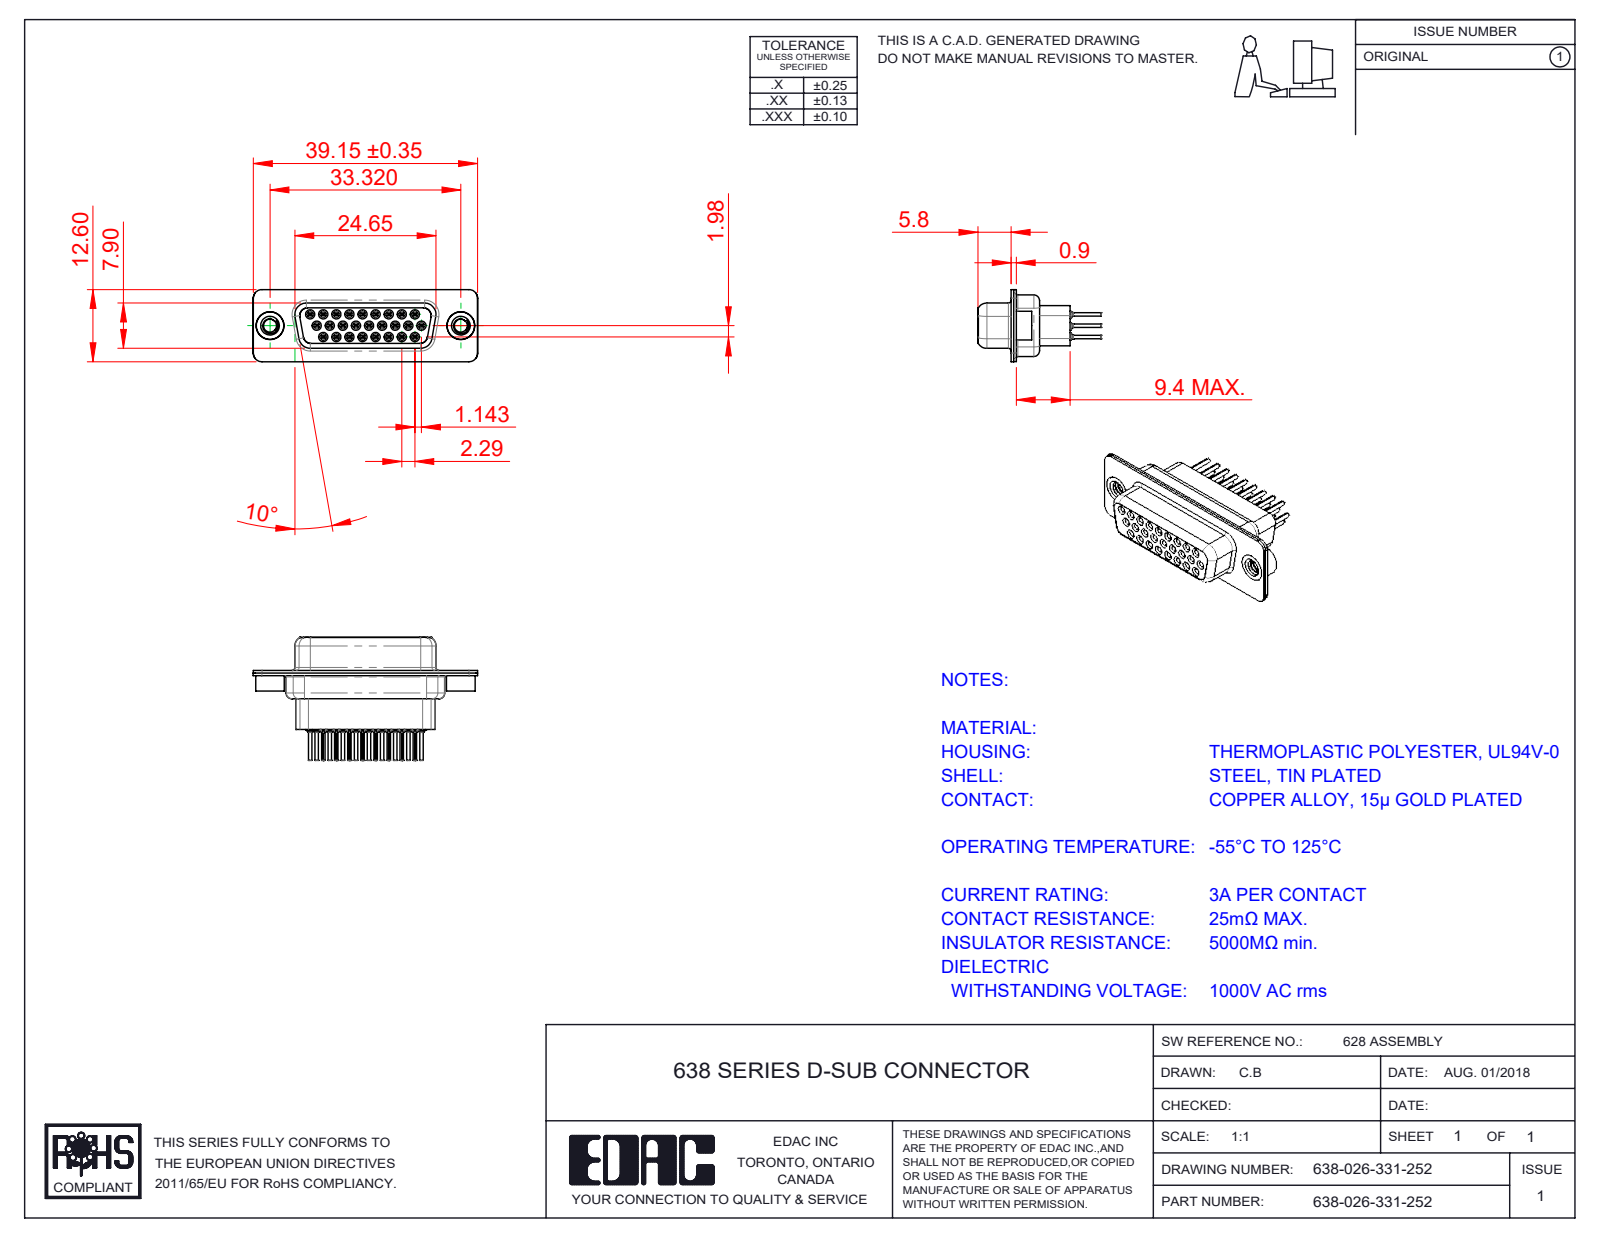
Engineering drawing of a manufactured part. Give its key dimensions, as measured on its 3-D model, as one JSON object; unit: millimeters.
{"part_name": "638 Shell Rear_26 Contacts; 638 Contact Row 1_31; 638 Housing_26 Contacts HP; 638 Contact Row 2_31 (+4 more)", "step_written_by": "SolidWorks 2020 (CONFIG_CONTROL_DESIGN)", "units": "millimeters", "bodies": {"solids": 31, "faces": 3477, "planar": 873, "cylindrical": 995, "other": 1609}, "overall_size": [39.19, 21.5, 12.6], "volume_mm3": 2677, "surface_area_mm2": 9873, "round_holes": [[0.2, 26], [0.8, 26], [1, 26], [1.1, 26], [1.6, 26], [1.7, 26], [1.8, 26], [2.26, 2], [4, 2], [4.05, 2], [4.85, 2]], "round_bosses_or_shafts": [[2, 26], [1.5, 26], [1.2, 26], [0.6, 26], [5, 2], [4.95, 2], [4.8, 2]], "partial_cylinders_radius": [[0.1, 52], [1.5, 20], [0.28, 18], [2, 12], [1.55, 8], [1.35, 5], [0.25, 4], [0.5, 4]], "face_to_face_distances": [0.45, 0.4, 6.6, 0.9, 1.43, 8.88, 7, 2.28, 9.4, 5.8], "hole_center_spacings": [3.96, 2.28, 4.57, 6.05, 2.29, 8.24, 6.86, 10.48]}
